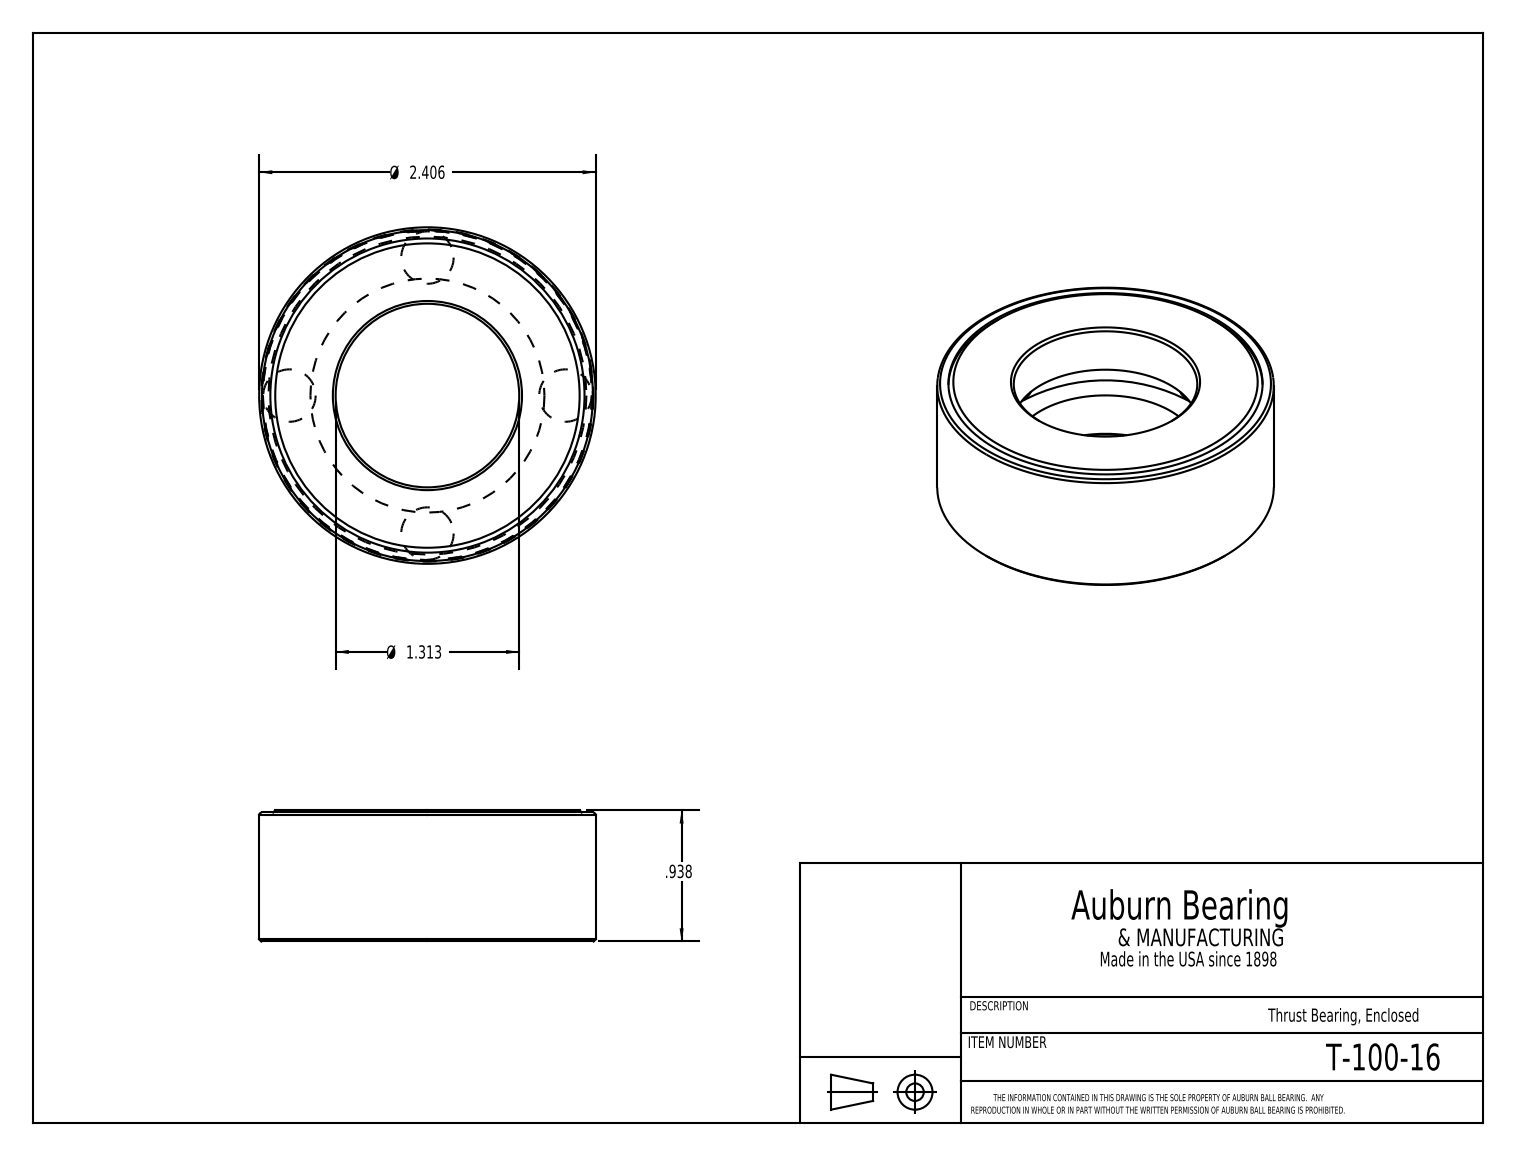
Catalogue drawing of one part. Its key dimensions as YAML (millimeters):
part_name: "T-100-16"
step_written_by: "SolidWorks 2016 (CONFIG_CONTROL_DESIGN)"
units: millimeters
bodies: {solids: 6, faces: 28, planar: 9, cylindrical: 7, other: 12}
overall_size: [61.1, 61.1, 23.8]
volume: 35760
surface_area: 20500
round_holes:
  - {diameter: 33.4, count: 1}
  - {diameter: 57, count: 1}
  - {diameter: 60.1, count: 1}
round_bosses_or_shafts:
  - {diameter: 61.1, count: 1}
  - {diameter: 59.7, count: 1}
face_to_face_distances: [9, 14.8, 23.8, 5.7, 22.9, 23.4, 13.9, 14.4, 8.2, 8.7]
